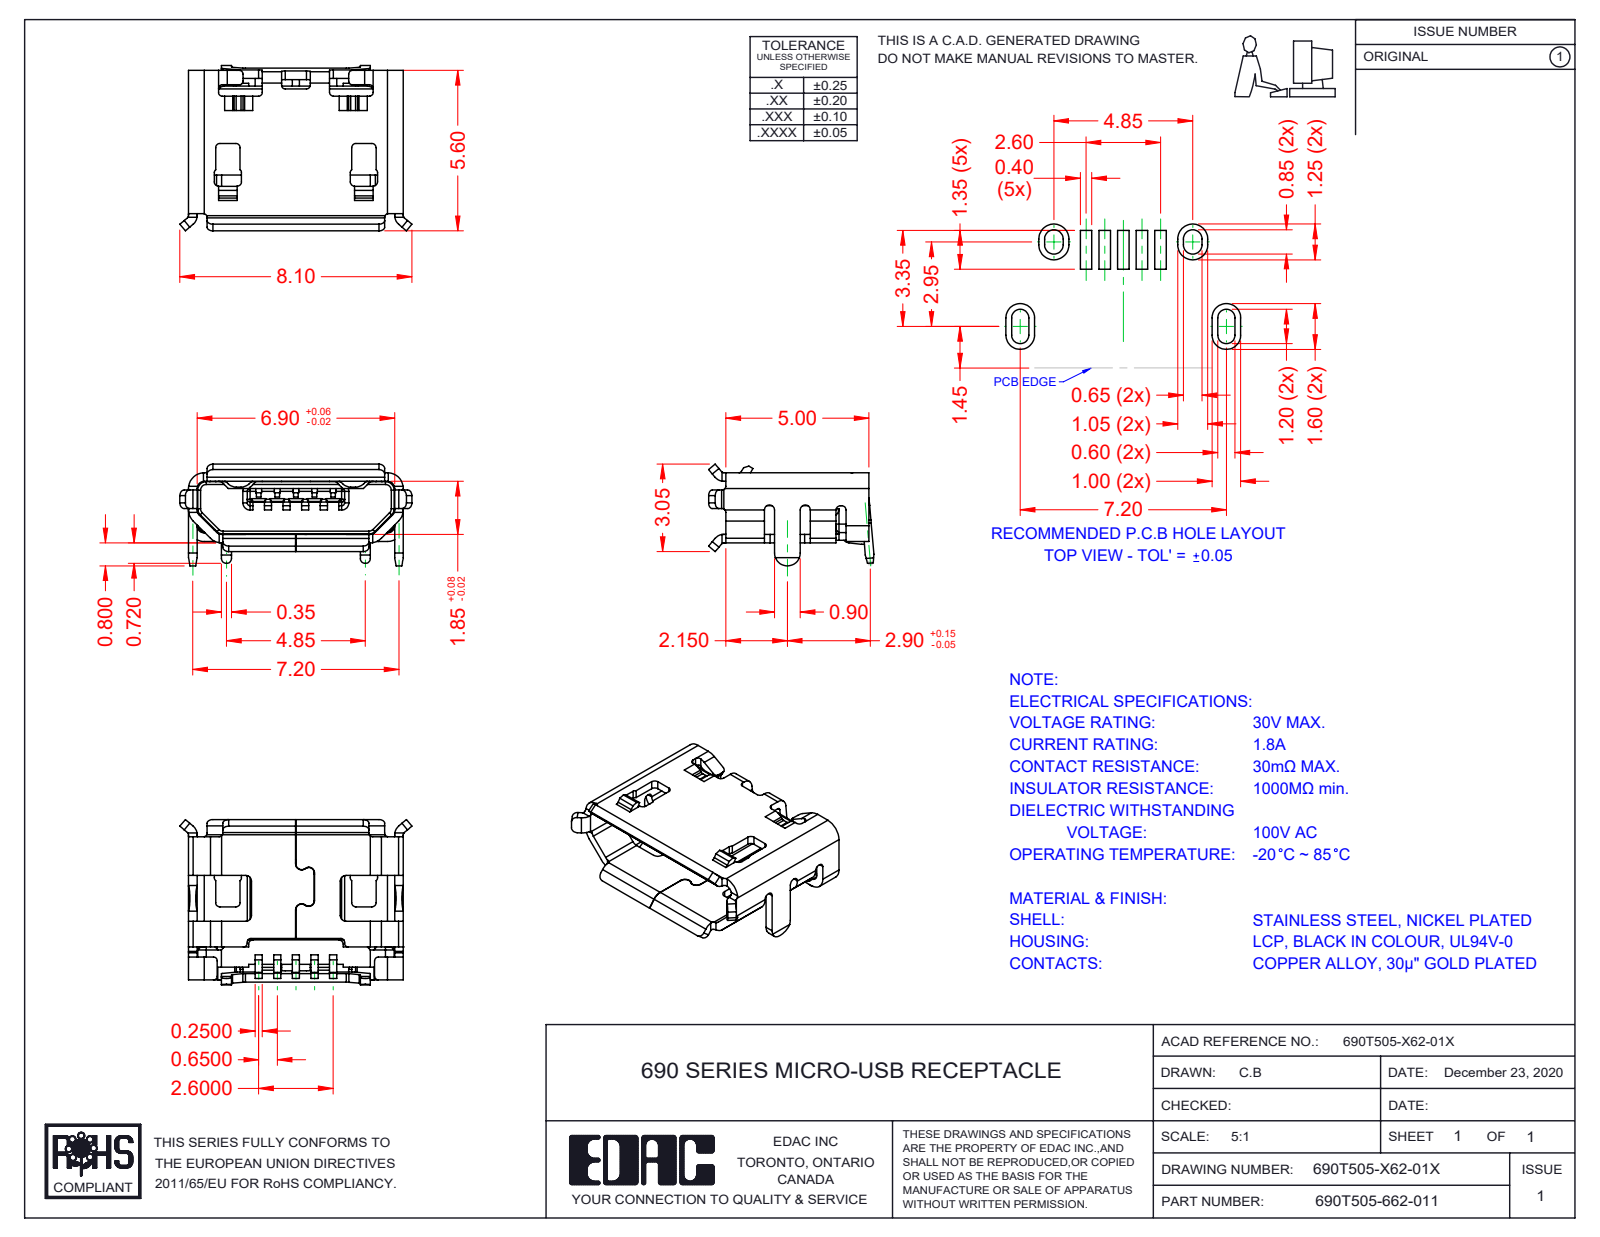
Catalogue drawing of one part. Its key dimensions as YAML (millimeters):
part_name: "690T505-162-011; SHELL 690T505-X62-01X; Insulator 690T505-X62-01X"
step_written_by: "SolidWorks 2020 (AUTOMOTIVE_DESIGN)"
units: millimeters
bodies: {solids: 2, faces: 653, planar: 415, cylindrical: 199, other: 39}
overall_size: [8.1, 5.77, 3.55]
volume: 43
surface_area: 279
partial_cylinders:
  - {radius: 0.13, count: 42}
  - {radius: 0.1, count: 26}
  - {radius: 0.15, count: 20}
  - {radius: 0.2, count: 16}
  - {radius: 0.4, count: 13}
  - {radius: 0.3, count: 11}
  - {radius: 0.25, count: 10}
  - {radius: 0.55, count: 9}
face_to_face_distances: [2.15, 1.85, 2.45, 0.95, 7.2, 1.5, 0.55, 0.9, 0.35, 0.6]
